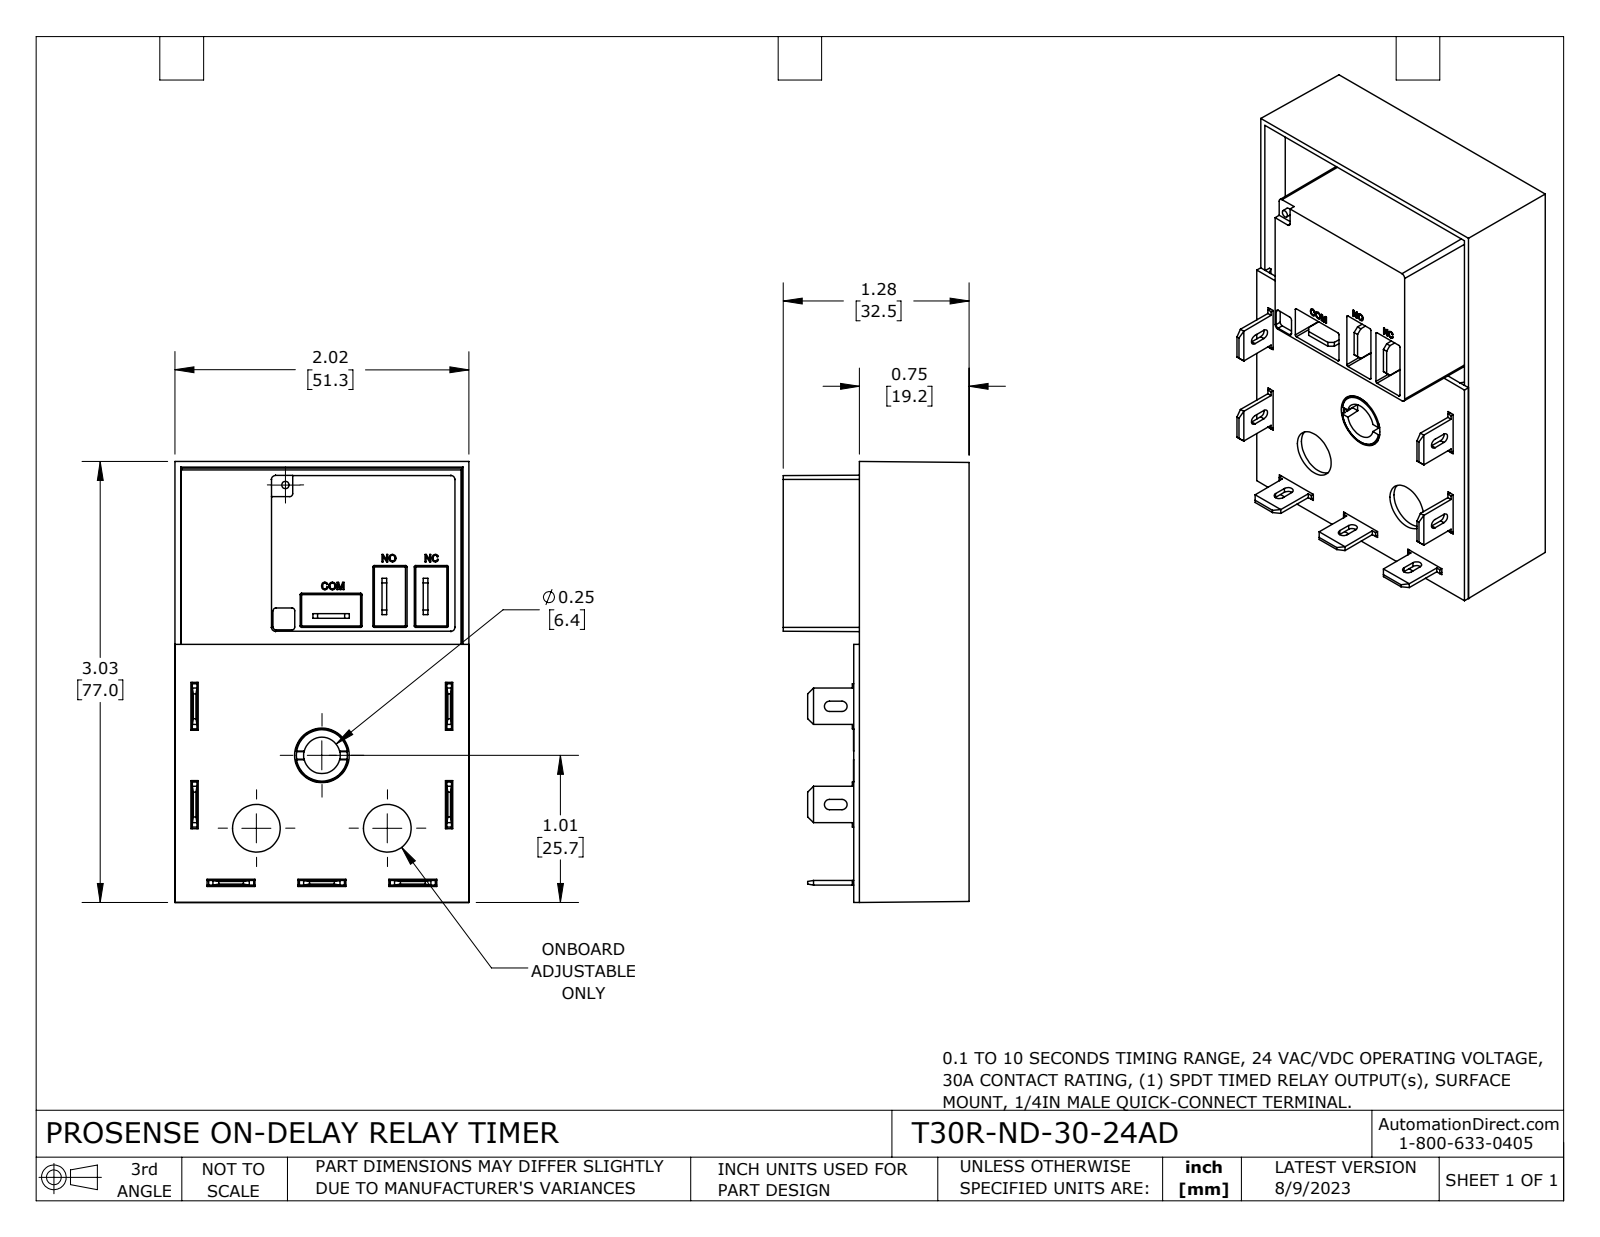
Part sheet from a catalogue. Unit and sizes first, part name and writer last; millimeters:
Units: millimetres
Overall size (bounding box): 77 × 51.3 × 32.5
Round holes (diameter × count): ⌀8.3 ×2, ⌀8.9 ×1, ⌀9.5 ×1
Round bosses / shafts (diameter × count): ⌀9.3 ×1, ⌀1.3 ×1
Partial cylindrical surfaces — rounded edges, fillets, slot ends (radius × count): R0.3 ×21, R0.5 ×15, R0.9 ×10
Main face-to-face distances: 1.5, 14.1, 12.6, 1, 19.2, 17.7, 5, 1, 18.6, 20.1
Hole centre spacings: 17.1, 22.9
Volume: 81 050 mm³ · Surface area: 42 960 mm²
Bodies: 11 solids, 622 faces (493 planar, 69 cylindrical, 60 other)
Part name (STEP PRODUCT): T30R-ND-30-24AD
STEP written by: SolidWorks 2021 (CONFIG_CONTROL_DESIGN)
